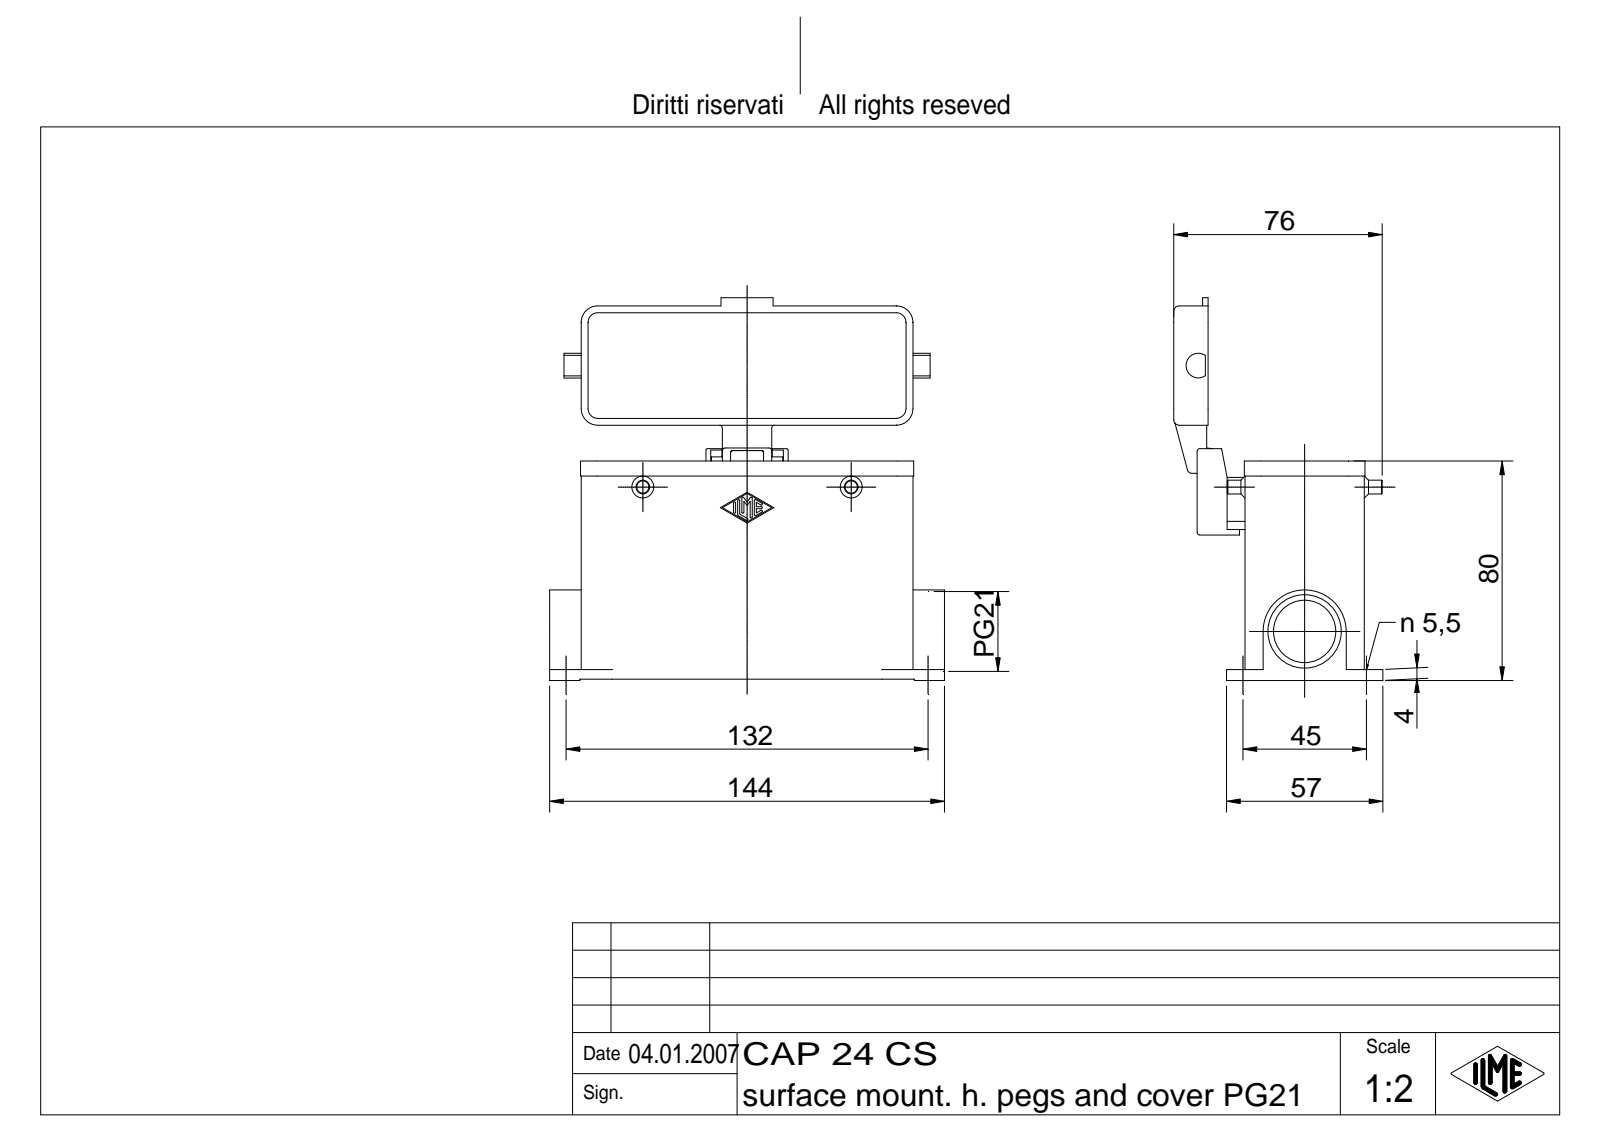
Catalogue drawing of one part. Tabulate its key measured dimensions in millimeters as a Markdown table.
| quantity | value |
| --- | --- |
| part name | CAP 24 CS |
| STEP written by | Autodesk Inventor 7 (AUTOMOTIVE_DESIGN) |
| units | millimeters |
| bodies | 2 solids, 475 faces (177 planar, 177 cylindrical, 121 other) |
| overall size | 144 × 139.5 × 76.25 |
| volume | 162 396 mm³ |
| surface area | 88 802 mm² |
| round holes (diameter × count) | 5.5 × 4, 4 × 1, 5 × 1, 22.78 × 1, 26.78 × 1 |
| round bosses / shafts (diameter × count) | 5 × 2, 3 × 2, 7 × 1, 4 × 1 |
| partial cylindrical surfaces (radius × count) | 1 × 26, 0.38 × 14, 6 × 12, 0.5 × 9, 0.7 × 8, 2 × 8, 3 × 4, 3.5 × 4 |
| main face-to-face distances | 3, 40.5, 43.5, 3.5, 37.5, 69.5, 66.5, 22.5, 29, 26 |
| hole center spacings | 45, 132, 139.46 |
